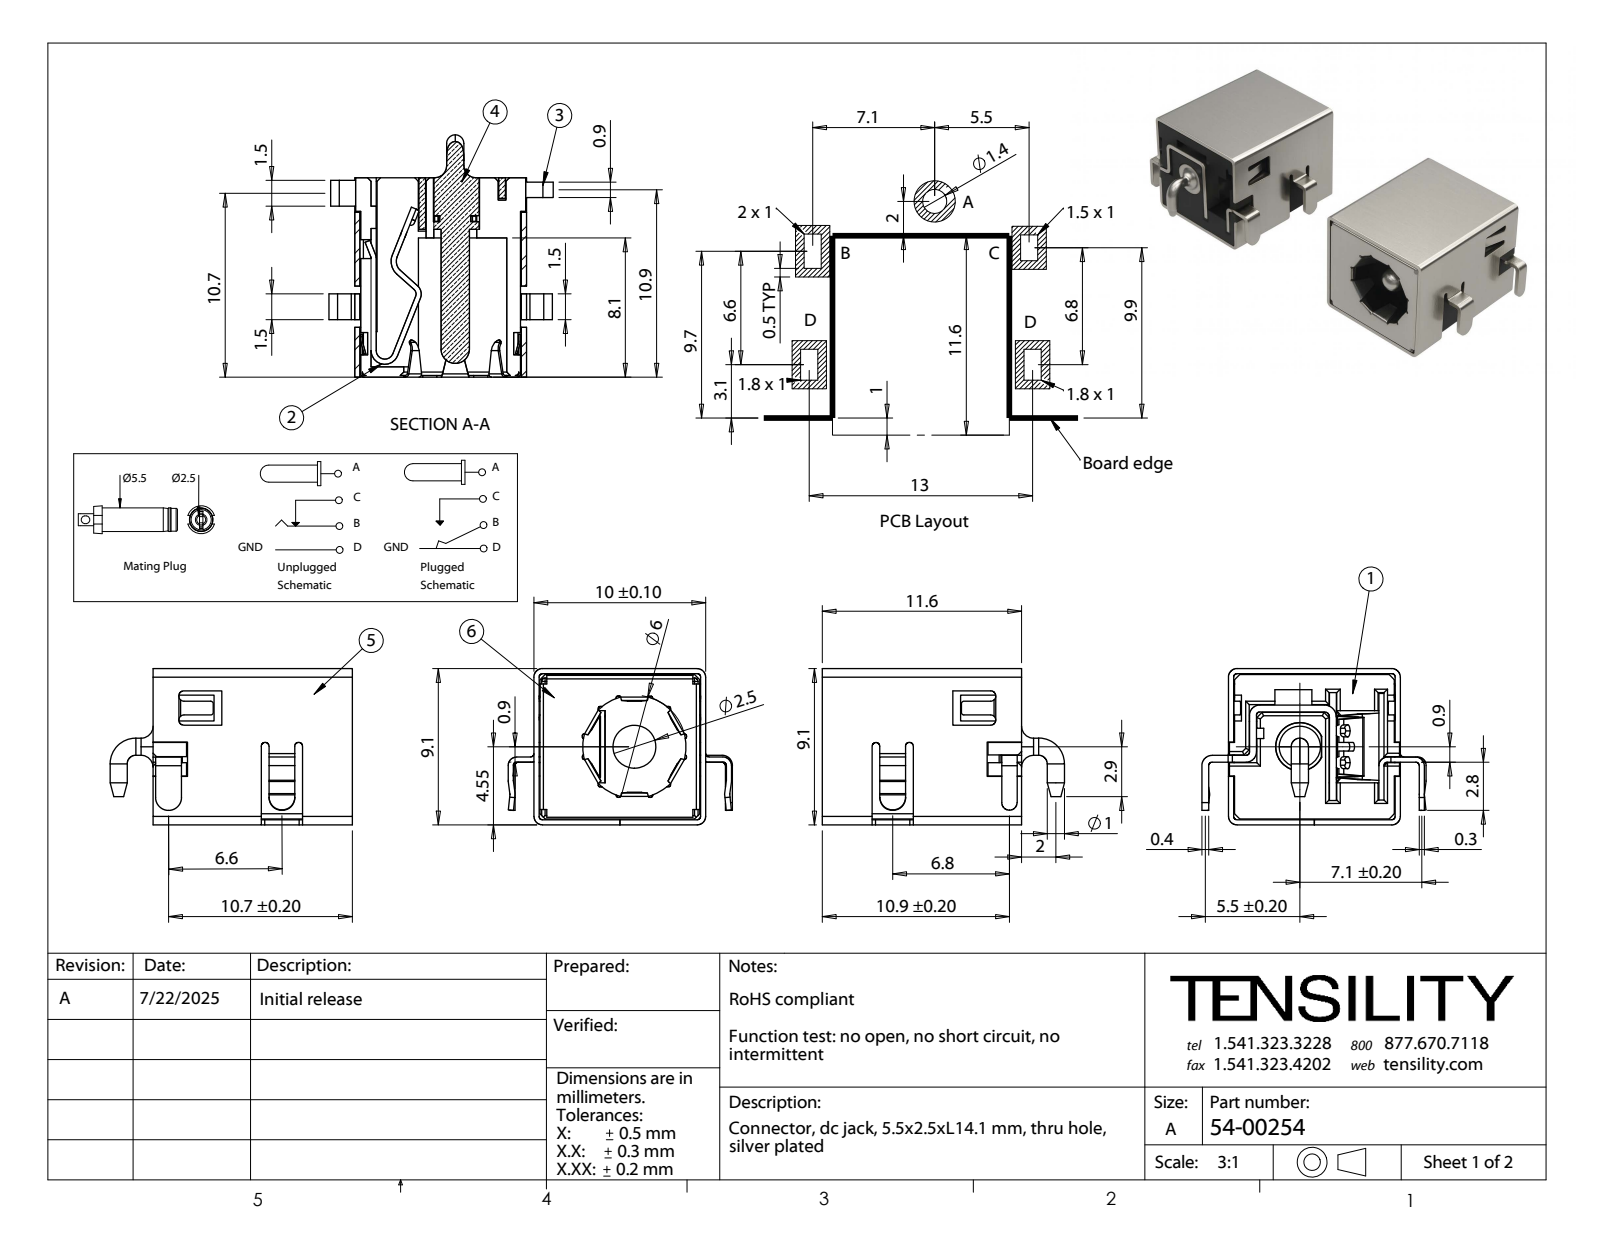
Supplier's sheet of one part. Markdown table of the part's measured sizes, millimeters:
| quantity | value |
| --- | --- |
| part name | 54-00254_revA |
| STEP written by | SolidWorks 2015 (CONFIG_CONTROL_DESIGN) |
| units | millimeters |
| bodies | 1 solid, 733 faces (430 planar, 235 cylindrical, 68 other) |
| overall size | 14.1 × 13.05 × 9.1 |
| volume | 715 mm³ |
| surface area | 2 204 mm² |
| round holes (diameter × count) | 2.82 × 1, 6 × 1 |
| round bosses / shafts (diameter × count) | 1 × 2, 2.8 × 1, 2.5 × 1, 1.8 × 1 |
| partial cylindrical surfaces (radius × count) | 0.2 × 54, 0.3 × 34, 0.15 × 18, 0.5 × 15, 0.6 × 11, 0.1 × 10, 0.7 × 8, 0.29 × 4 |
| main face-to-face distances | 0.35, 8.75, 8.45, 8.8, 8.4, 9.7, 9.35, 9.65, 8.5, 9.1 |
